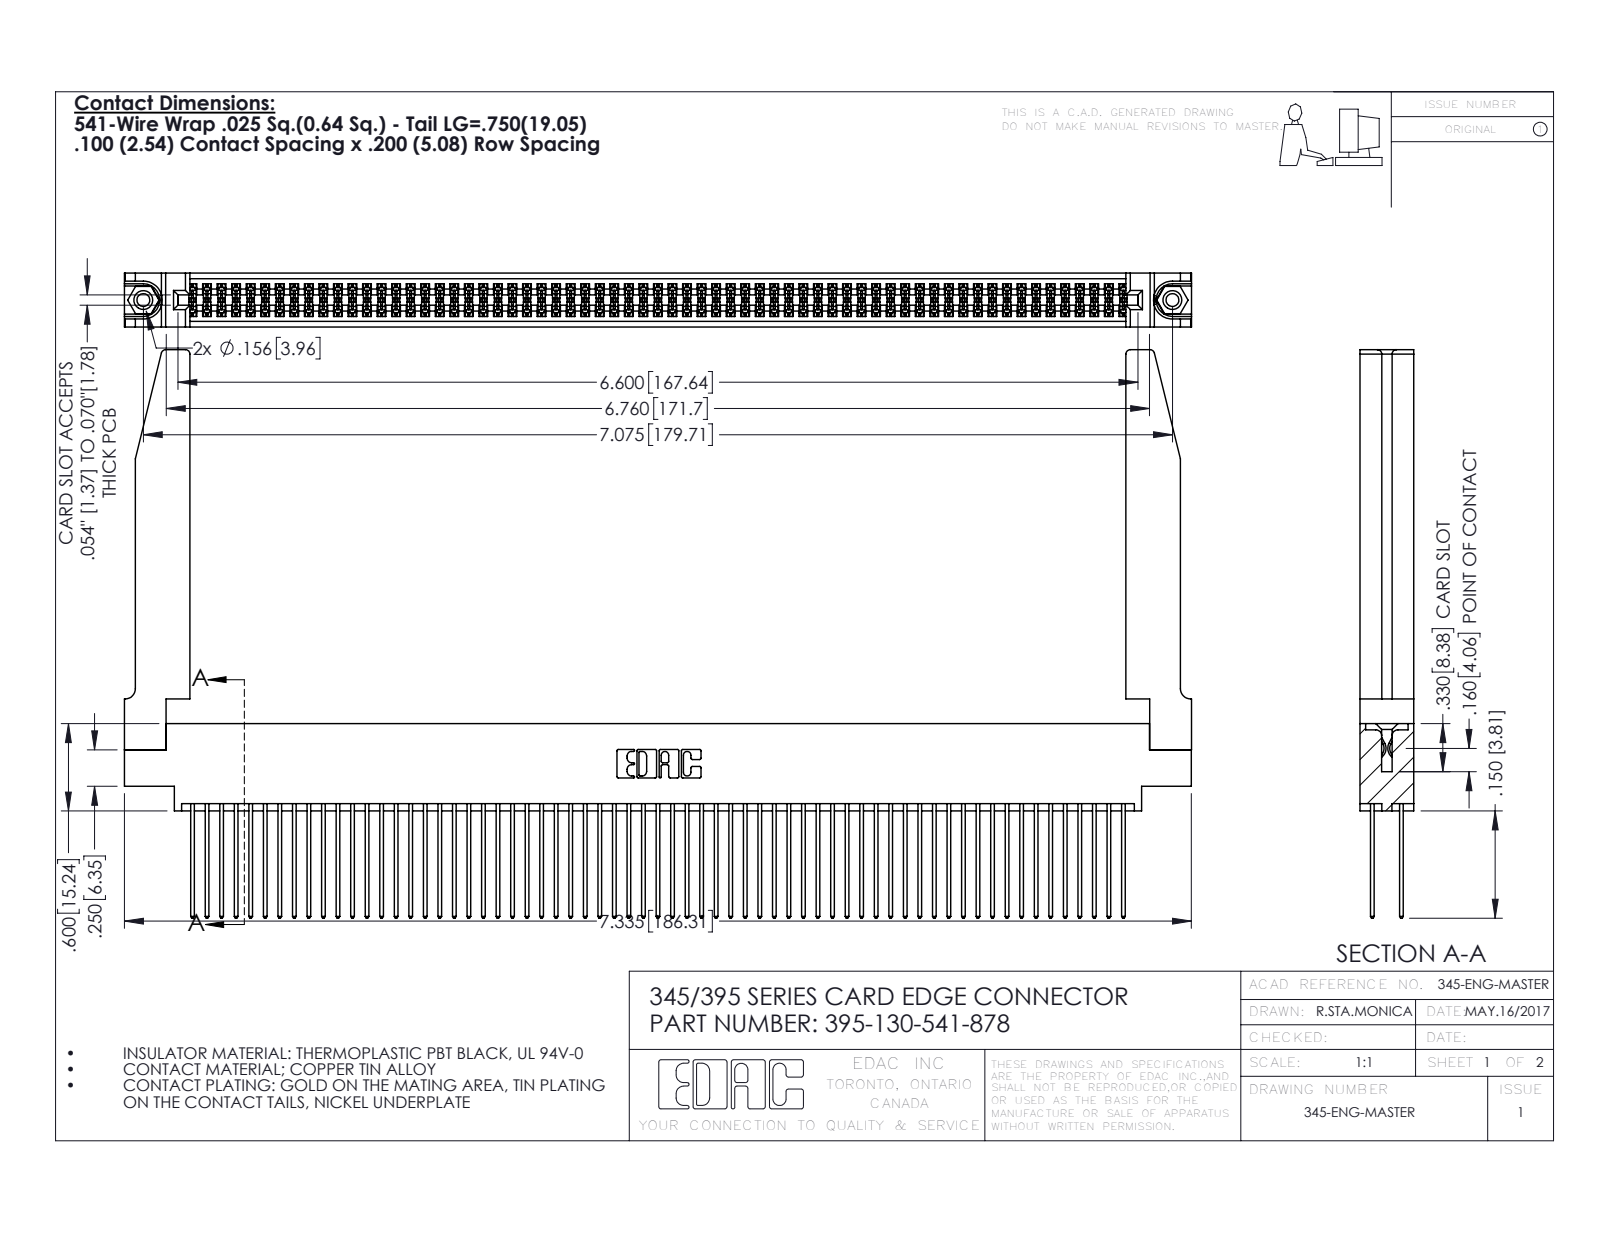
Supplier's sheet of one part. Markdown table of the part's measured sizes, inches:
| quantity | value |
| --- | --- |
| part name | 345-250-001_345-250-001-102; 345-292-001_345-293-141; 395-130-541-878; 345 Part_0.170 Offset - 0.156 Dia-TH (+1 more) |
| STEP written by | SolidWorks 2016 (CONFIG_CONTROL_DESIGN) |
| units | inches |
| bodies | 135 solids, 6864 faces (4516 planar, 2296 cylindrical, 52 other) |
| overall size | 7.336 × 3.907 × 0.37 |
| volume | 1.63 in³ |
| surface area | 60.36 in² |
| round holes (diameter × count) | 0.089 × 2, 0.125 × 2, 0.156 × 2, 0.064 × 1 |
| round bosses / shafts (diameter × count) | 0.155 × 2 |
| partial cylindrical surfaces (radius × count) | 0.006 × 195, 0.01 × 130, 0.01 × 22, 0.03 × 8, 0.007 × 6, 0.031 × 6, 0.026 × 3, 0.014 × 2 |
| main face-to-face distances | 0.072, 0.298, 0.37, 0.098, 0.272, 0.025, 0.2, 0.225, 0.175, 0.148 |
| hole center spacings | 0.27, 6.839, 7.075 |
